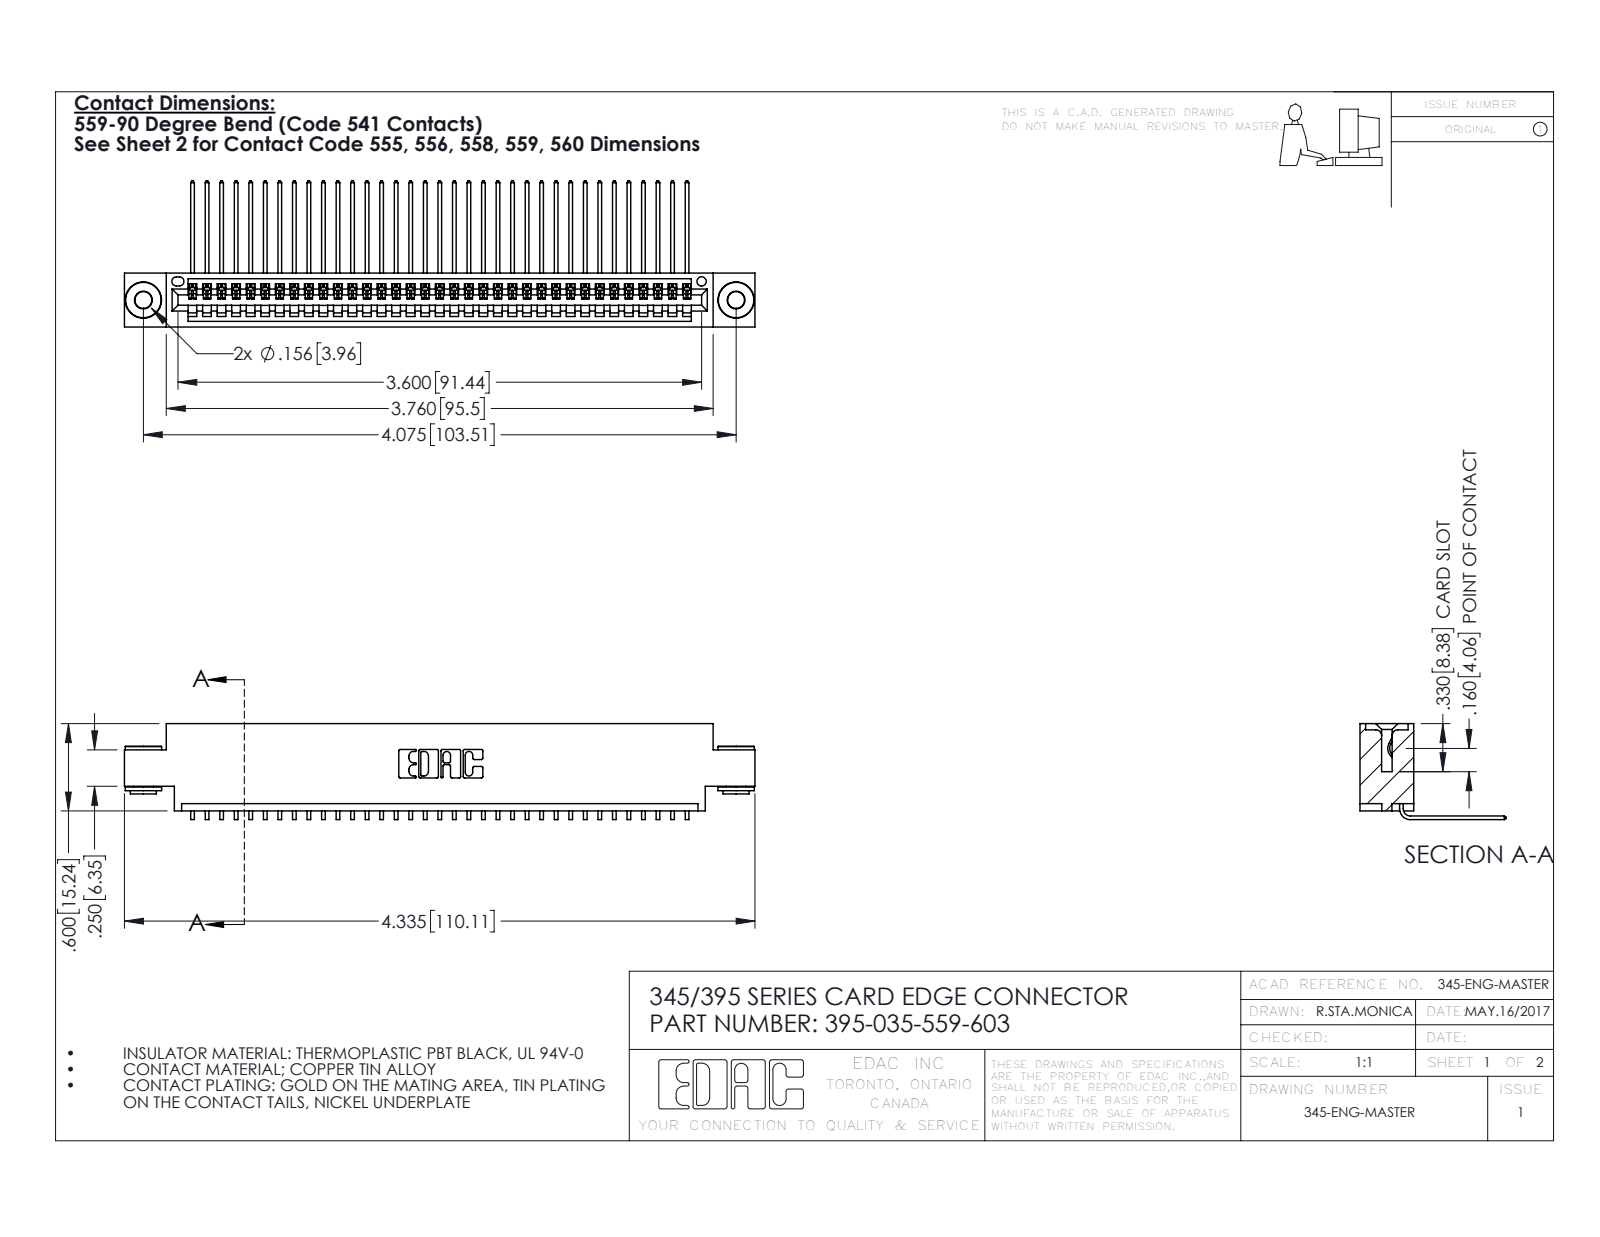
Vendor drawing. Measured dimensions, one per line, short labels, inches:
name: 395-035-559-603; 345-250-002_345-250-002-102; 345-292-001_558 559 Tail - 1; 345 Part_0.170 Offset - 0.156 Dia-TH
written by: SolidWorks 2016 (CONFIG_CONTROL_DESIGN)
unit: in
bodies: 38 solids, 2268 faces (1564 planar, 696 cylindrical, 8 other)
size: 4.335 × 1.005 × 0.659
volume: 0.636 in³; area: 22.91 in²
holes: 2× ⌀0.116, 2× ⌀0.156, 1× ⌀0.064
bosses: 2× ⌀0.25, 2× ⌀0.18, 2× ⌀0.136
rounds: 70× R0.006, 22× R0.01, 6× R0.007, 6× R0.031, 3× R0.026, 2× R0.031, 2× R0.04, 1× R0.014
face distances: 0.072, 0.298, 0.37, 0.2, 0.098, 0.272, 0.025, 0.225, 0.175, 0.149
hole spacings: 0.27, 3.839, 4.075
